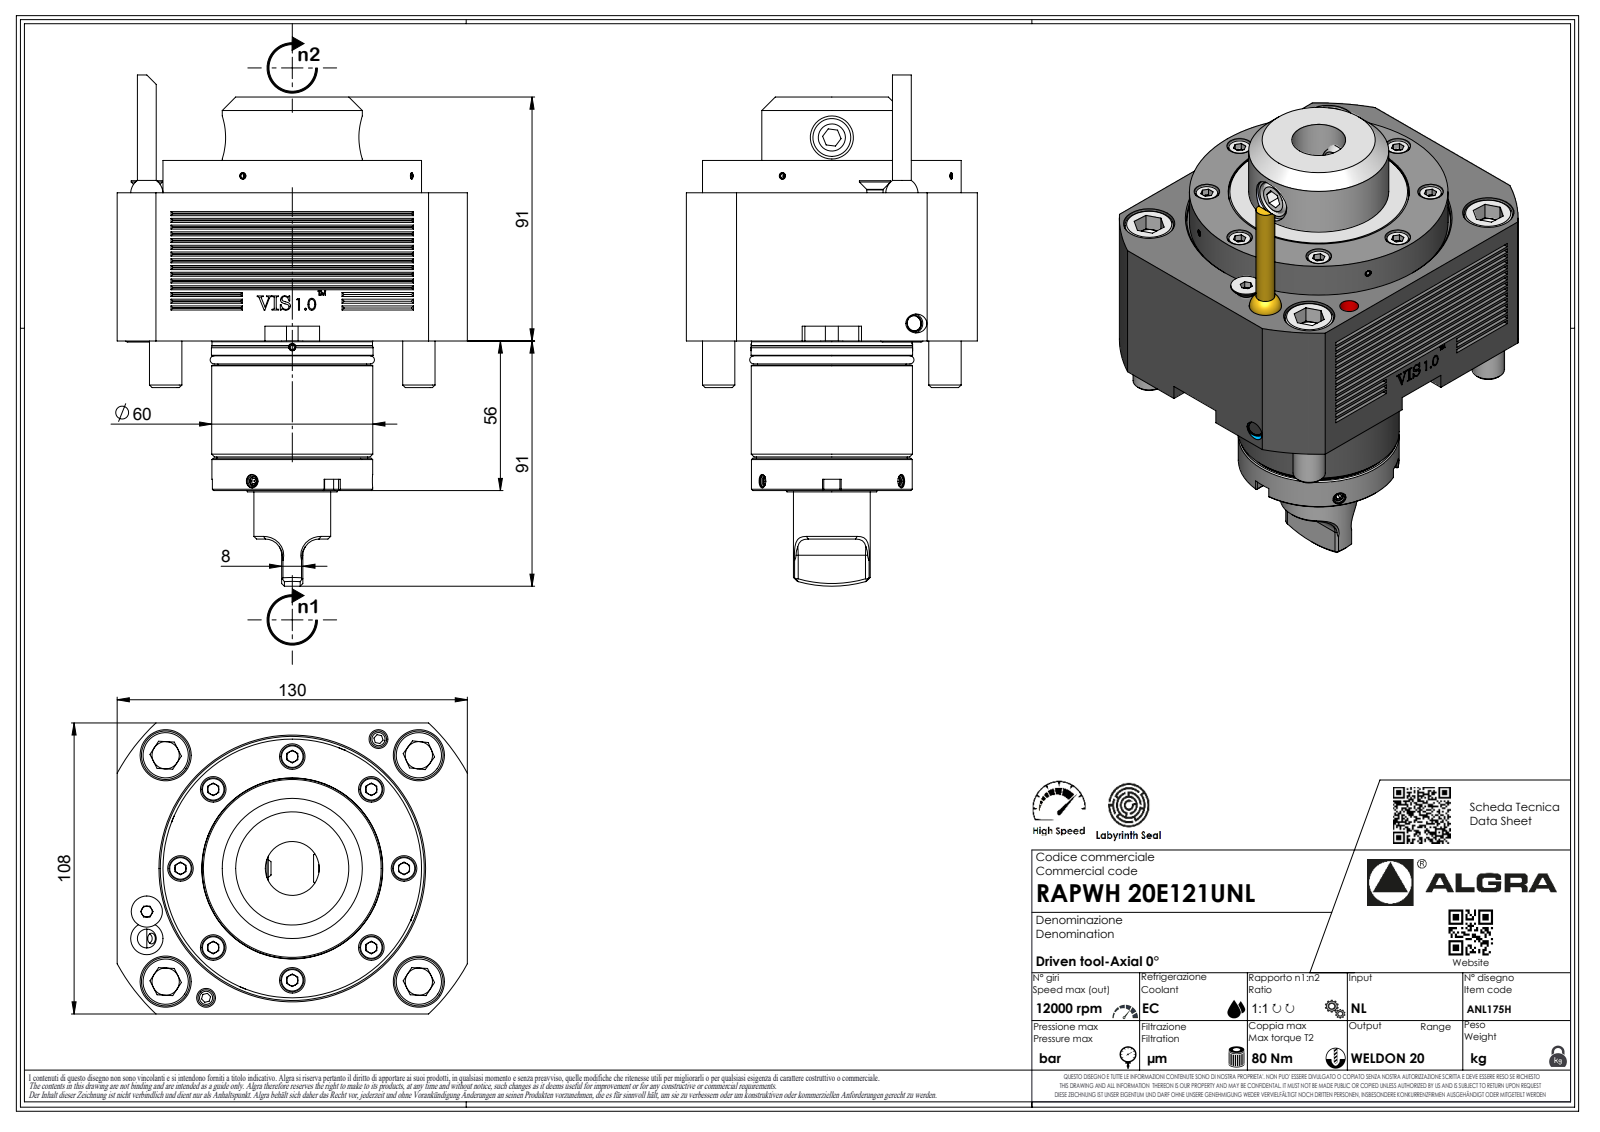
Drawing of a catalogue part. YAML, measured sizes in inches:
part_name: "RAPWH20E121UNL"
step_written_by: "SolidWorks 2023 (AUTOMOTIVE_DESIGN)"
units: inches
bodies: {solids: 1, faces: 396, planar: 263, cylindrical: 58, other: 75}
overall_size: [7.469, 5.118, 4.252]
volume: 64.26
surface_area: 117.1
round_holes:
  - {diameter: 0.083, count: 1}
  - {diameter: 0.157, count: 1}
round_bosses_or_shafts:
  - {diameter: 0.472, count: 4}
  - {diameter: 3.78, count: 1}
  - {diameter: 2.362, count: 1}
  - {diameter: 2.354, count: 1}
  - {diameter: 2.047, count: 1}
  - {diameter: 1.122, count: 1}
  - {diameter: 0.276, count: 1}
  - {diameter: 0.251, count: 1}
partial_cylinders:
  - {radius: 0.315, count: 8}
  - {radius: 0.013, count: 7}
  - {radius: 0.02, count: 7}
  - {radius: 0.146, count: 7}
  - {radius: 0.236, count: 6}
  - {radius: 0.008, count: 1}
  - {radius: 0.079, count: 1}
  - {radius: 1.811, count: 1}
face_to_face_distances: [2.165, 4.252, 2.638, 0.472, 5.118, 2.185, 4.35, 4.823, 2.421, 2.402]
